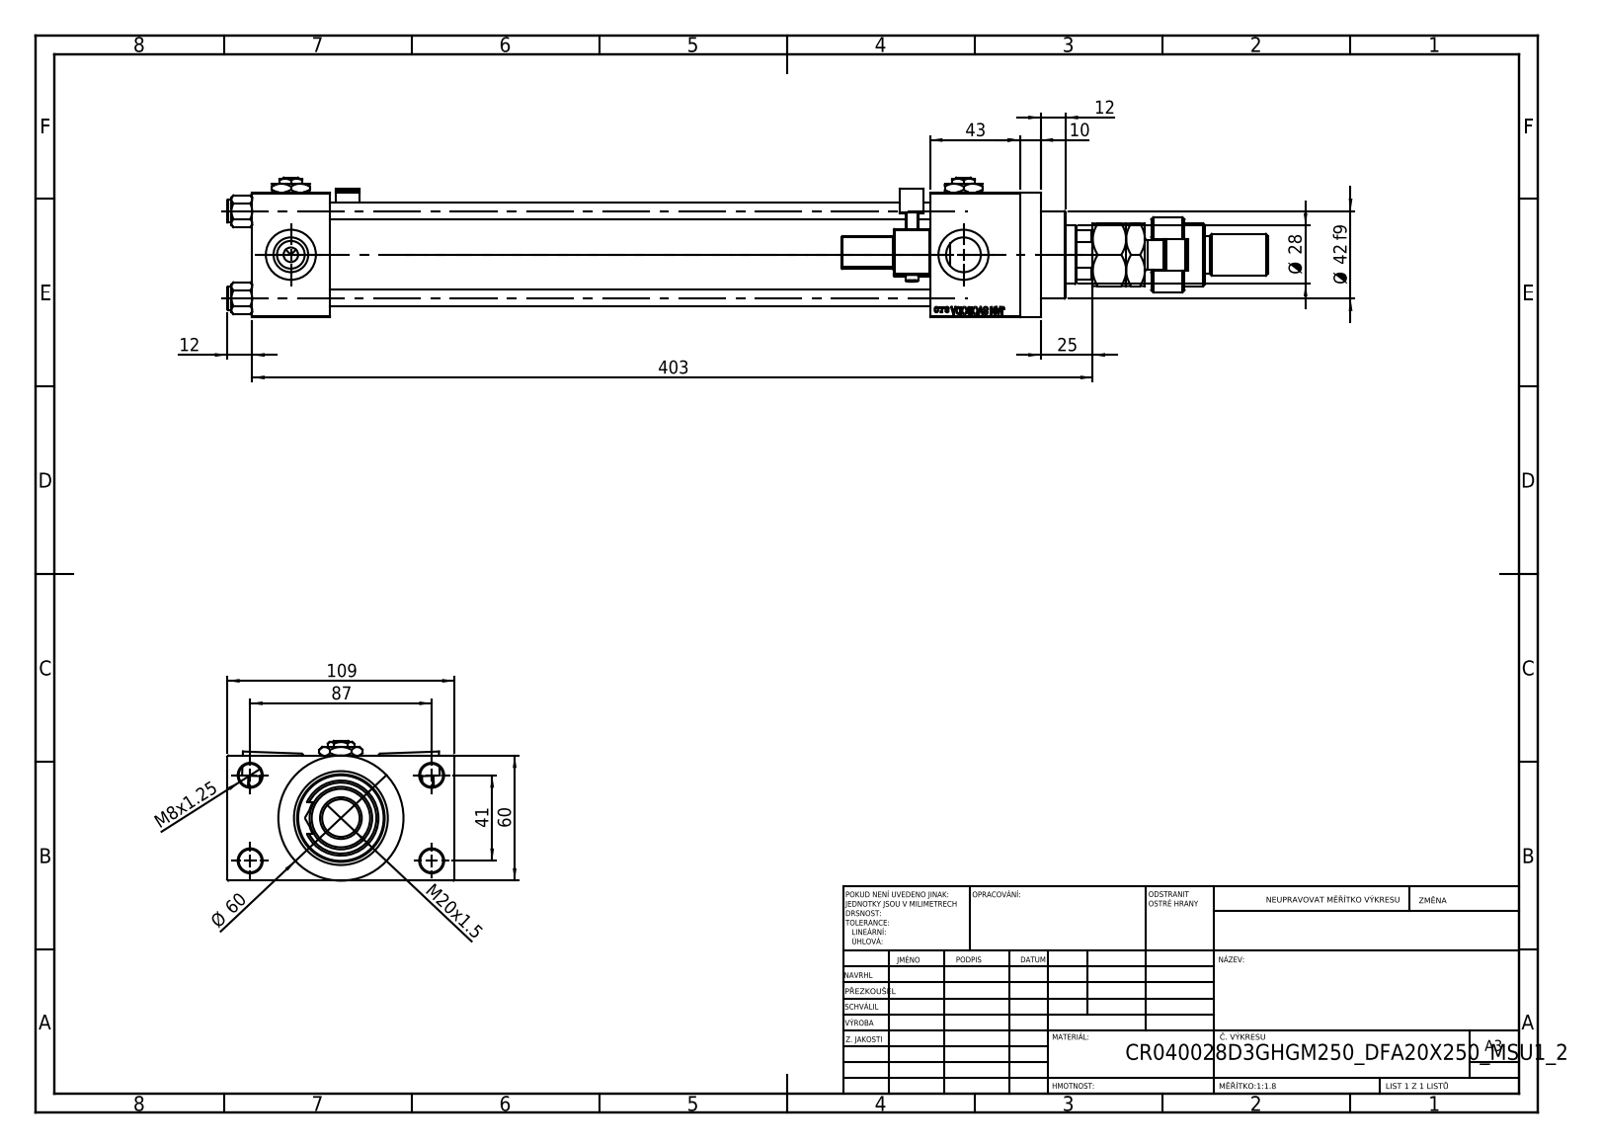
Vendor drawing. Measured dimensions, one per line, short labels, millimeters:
name: V215CR_D_Body; NUT_M5_D; MFA; V215CR_MSU (+5 more)
written by: SolidWorks 2019 (CONFIG_CONTROL_DESIGN)
unit: mm
bodies: 17 solids, 1444 faces (632 planar, 172 cylindrical, 640 other)
size: 499 × 109 × 67
volume: 897 524 mm³; area: 262 576 mm²
holes: 4× ⌀8, 4× ⌀11, 4× ⌀16.66, 4× ⌀24, 3× ⌀7, 1× ⌀18.5, 1× ⌀28, 1× ⌀31, 1× ⌀40, 1× ⌀45
bosses: 4× ⌀11, 2× ⌀6, 1× ⌀60, 1× ⌀46, 1× ⌀42, 1× ⌀36, 1× ⌀30, 1× ⌀22
rounds: 48× R0.5, 2× R1, 2× R2.5, 2× R4, 1× R7.5, 1× R12, 1× R13.5
face distances: 60, 288, 24.5, 84.5, 37, 325, 43, 368, 331, 109
hole spacings: 22.65, 29.49, 41.7, 47.15, 48.09, 64.35, 76.49, 41
